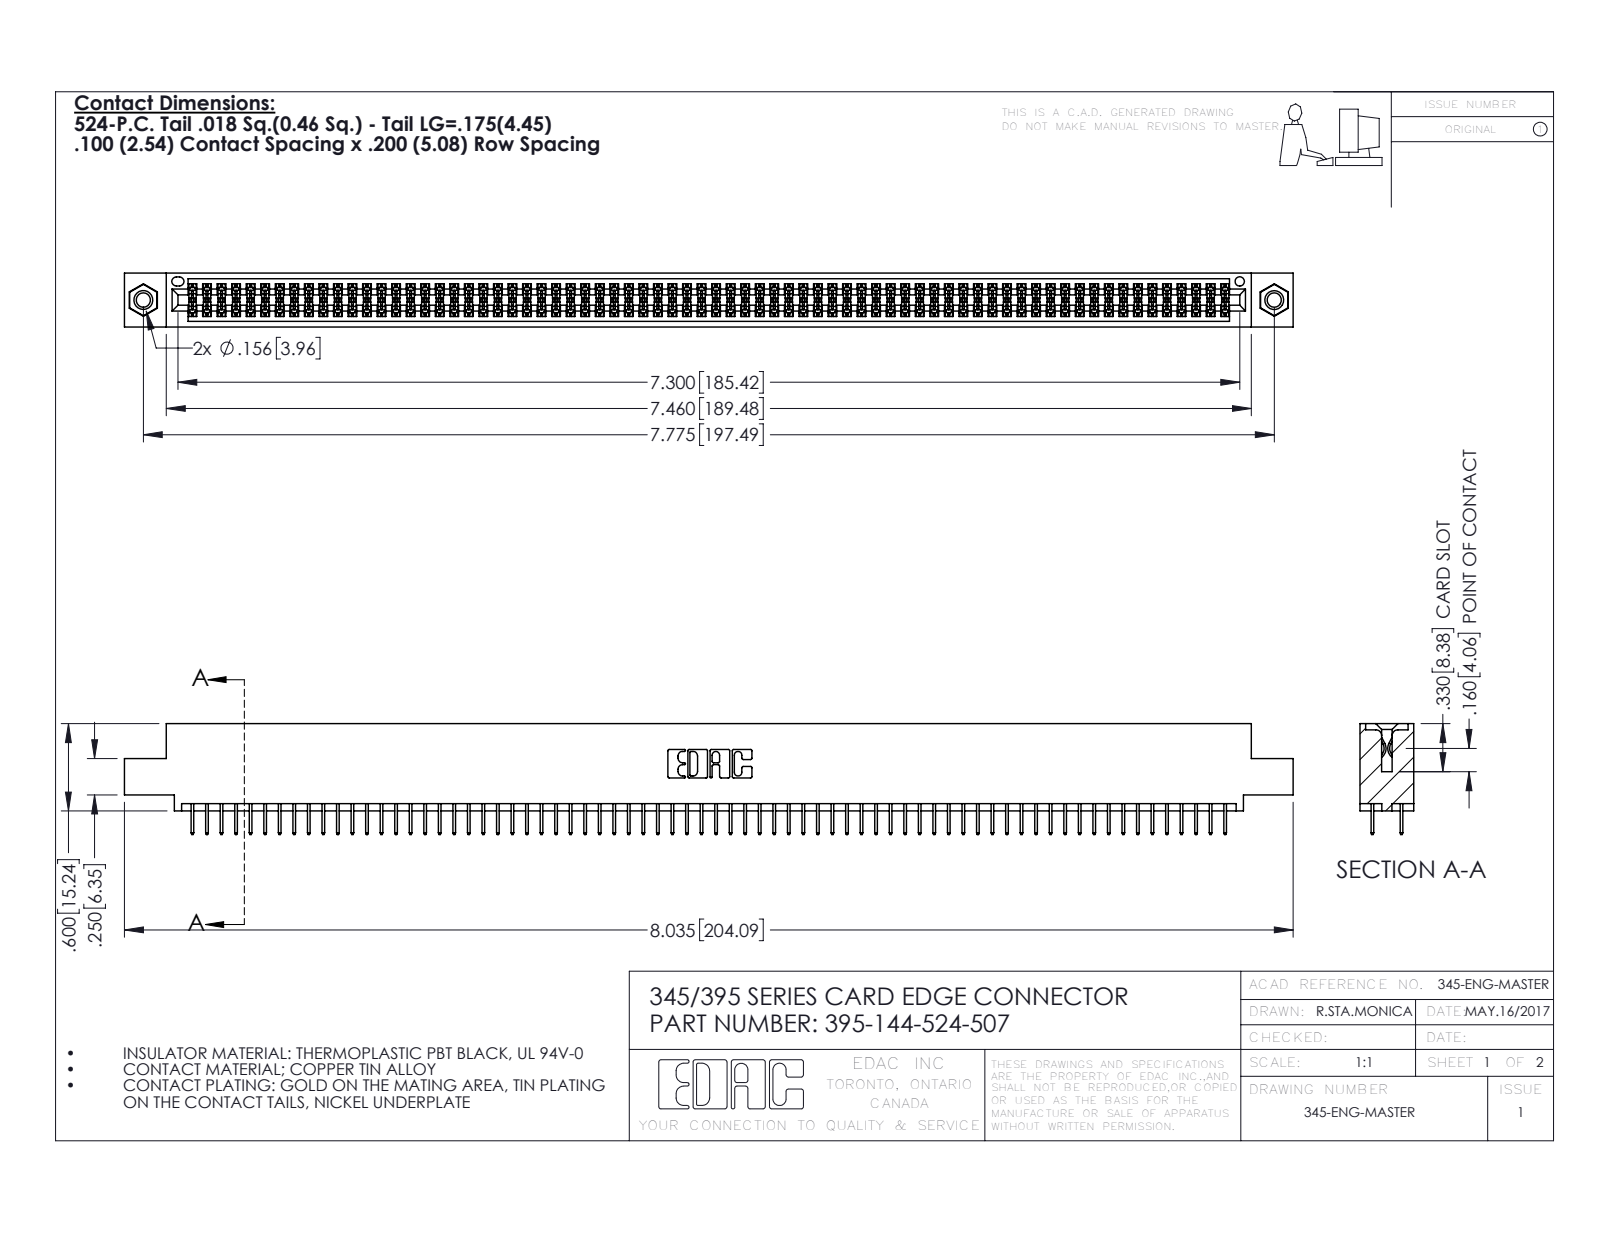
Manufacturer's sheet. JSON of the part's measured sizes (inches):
{"part_name": "345-250-001_345-250-005-103; 395-144-524-507; 345 Part_0.110 Offset - 0.156 Dia-TI; 345-292-001_345-293-124", "step_written_by": "SolidWorks 2016 (CONFIG_CONTROL_DESIGN)", "units": "inches", "bodies": {"solids": 147, "faces": 7966, "planar": 5732, "cylindrical": 2218, "other": 16}, "overall_size": [8.035, 0.762, 0.37], "volume_in3": 1.208, "surface_area_in2": 45.56, "round_holes": [[0.098, 2], [0.125, 2], [0.156, 2], [0.064, 1]], "round_bosses_or_shafts": [[0.155, 2]], "partial_cylinders_radius": [[0.006, 216], [0.01, 22], [0.007, 6], [0.031, 6], [0.026, 3], [0.014, 2], [0.019, 2], [0.022, 2]], "face_to_face_distances": [0.072, 0.298, 0.2, 0.37, 0.098, 0.272, 0.025, 0.225, 0.072, 0.175], "hole_center_spacings": [0.27, 7.539, 7.775]}
